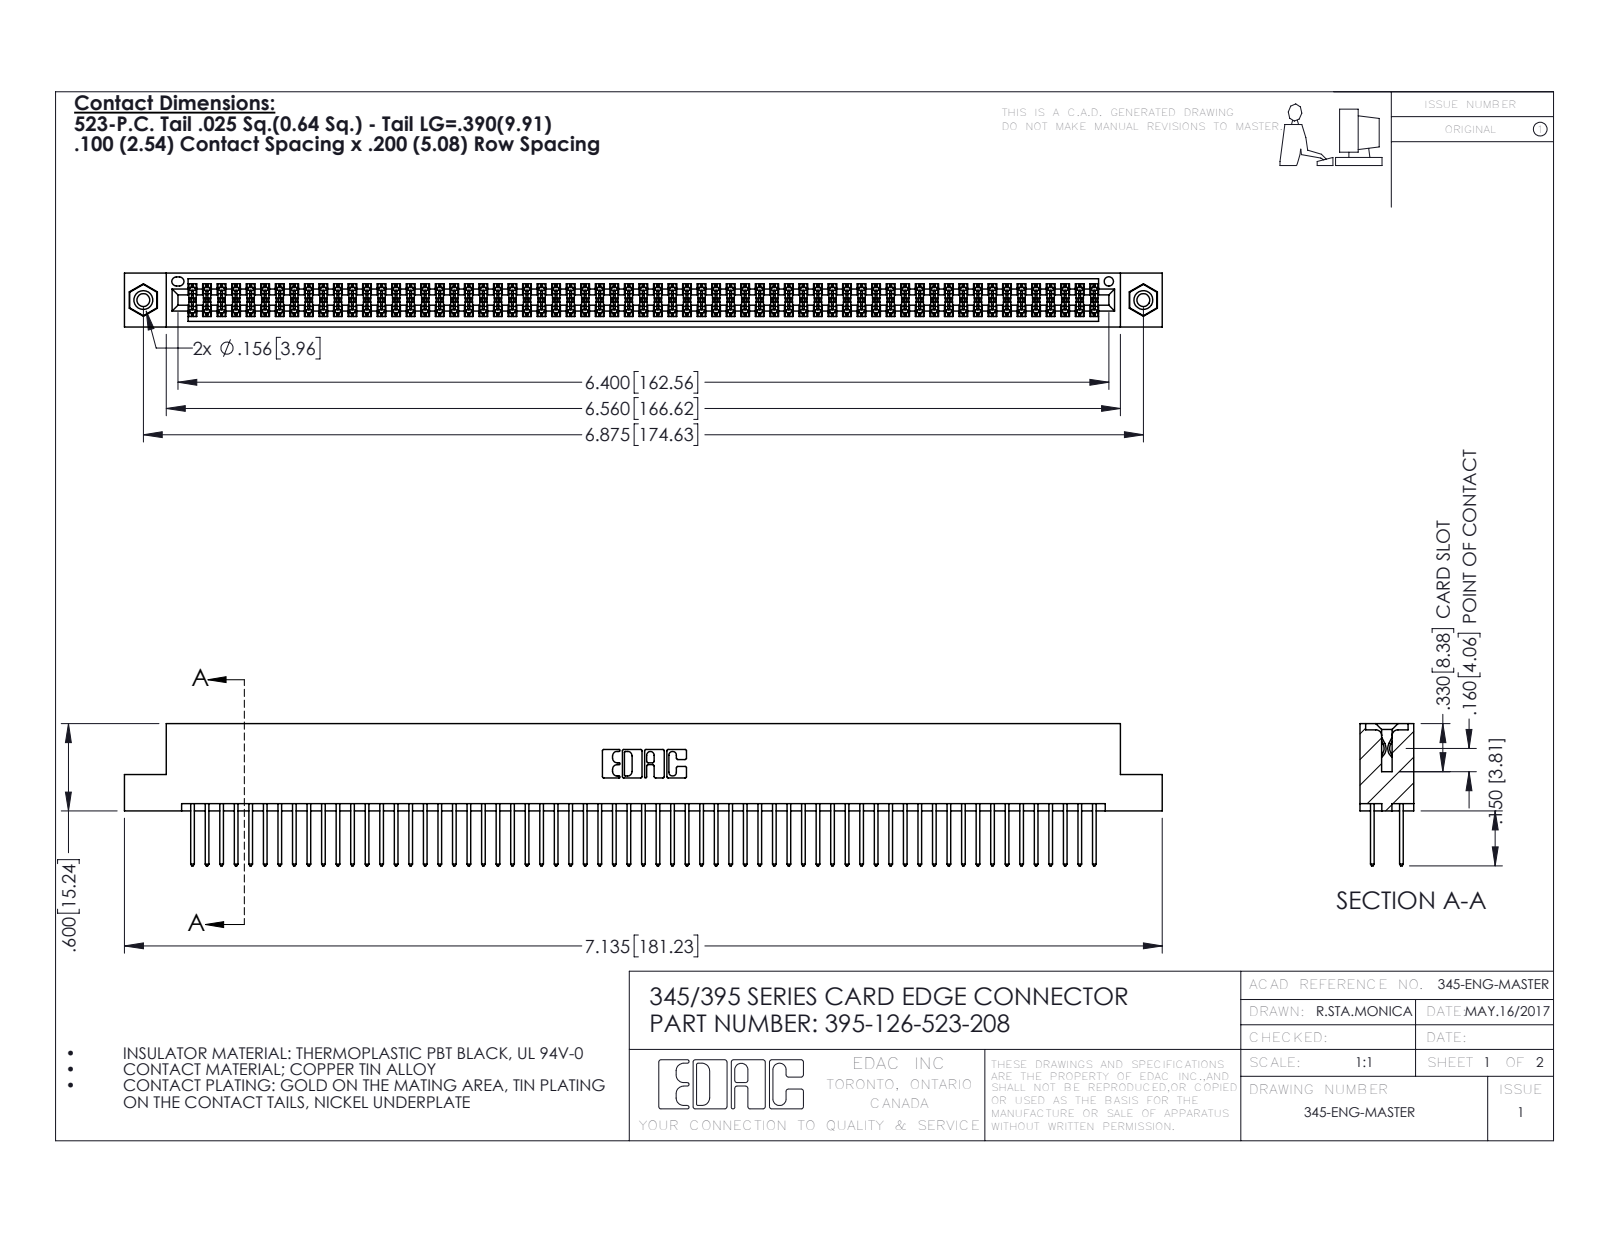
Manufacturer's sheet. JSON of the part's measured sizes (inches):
{"part_name": "345-250-001_345-250-003-102; 395-126-523-208; 345 Part_Flush Mounting Lugs - 0.156 Dia-TI; 345-292-001_345-293-123", "step_written_by": "SolidWorks 2016 (CONFIG_CONTROL_DESIGN)", "units": "inches", "bodies": {"solids": 129, "faces": 6486, "planar": 4270, "cylindrical": 2200, "other": 16}, "overall_size": [7.135, 0.977, 0.37], "volume_in3": 1.102, "surface_area_in2": 43.81, "round_holes": [[0.089, 2], [0.125, 2], [0.156, 2], [0.064, 1]], "round_bosses_or_shafts": [[0.155, 2]], "partial_cylinders_radius": [[0.006, 189], [0.01, 126], [0.01, 22], [0.007, 6], [0.031, 6], [0.026, 3], [0.014, 2], [0.019, 2]], "face_to_face_distances": [0.072, 0.298, 0.2, 0.098, 0.272, 0.025, 0.37, 0.225, 0.175, 0.149], "hole_center_spacings": [0.27, 6.639, 6.875]}
